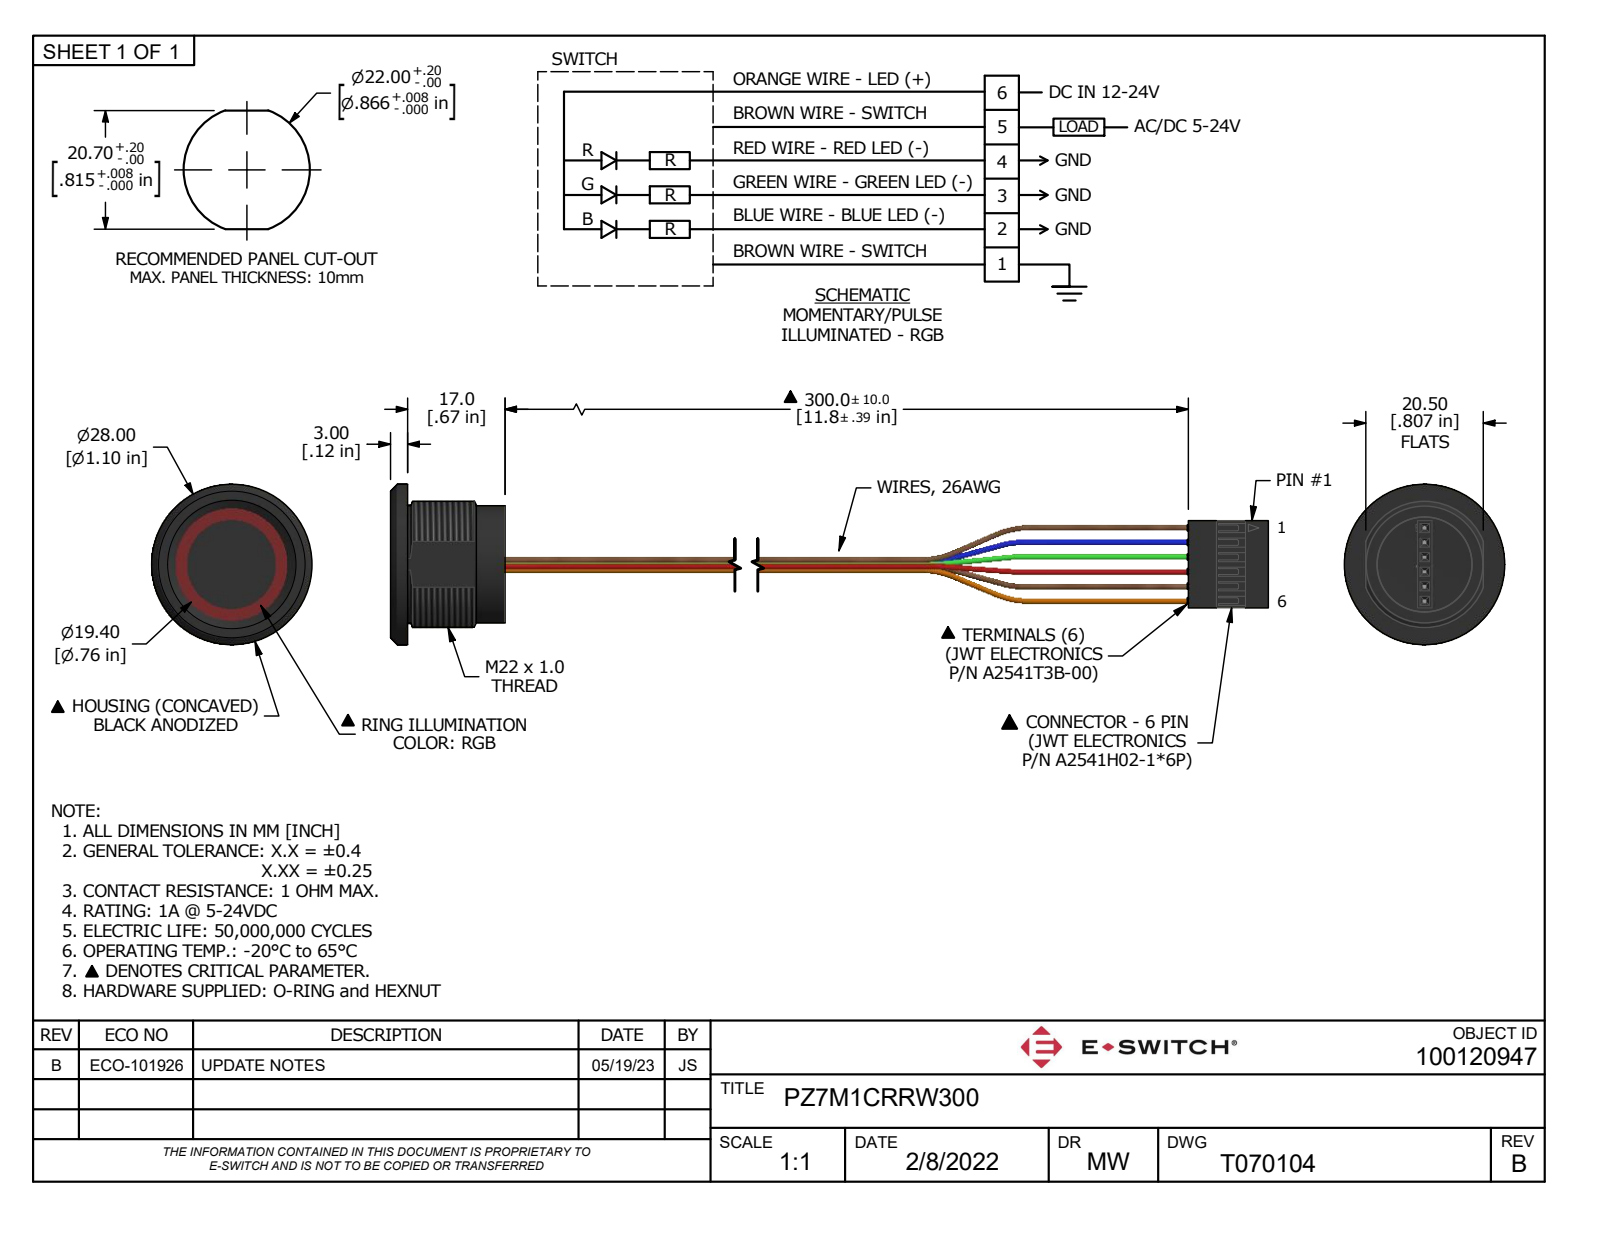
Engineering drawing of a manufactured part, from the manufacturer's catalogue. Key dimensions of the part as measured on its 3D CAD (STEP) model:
Part name (STEP PRODUCT): 100120947_Shrinkwrap_1
STEP written by: Autodesk Inventor 2020 (AUTOMOTIVE_DESIGN)
Units: millimetres
Bodies: 5 solids, 213 faces (141 planar, 47 cylindrical, 25 other)
Overall size (bounding box): 334 × 28 × 28
Volume: 9 260 mm³ · Surface area: 9 358 mm²
Round holes (diameter × count): ⌀19.4 ×1
Round bosses / shafts (diameter × count): ⌀1 ×16, ⌀0.7 ×6, ⌀28 ×1, ⌀20.6 ×1, ⌀20.4 ×1, ⌀15.4 ×1
Partial cylindrical surfaces — rounded edges, fillets, slot ends (radius × count): R0.25 ×12, R11 ×1
Main face-to-face distances: 2.54, 2.07, 0.47, 2, 8.98, 11.52, 1.6, 11.05, 9.45, 5.08
